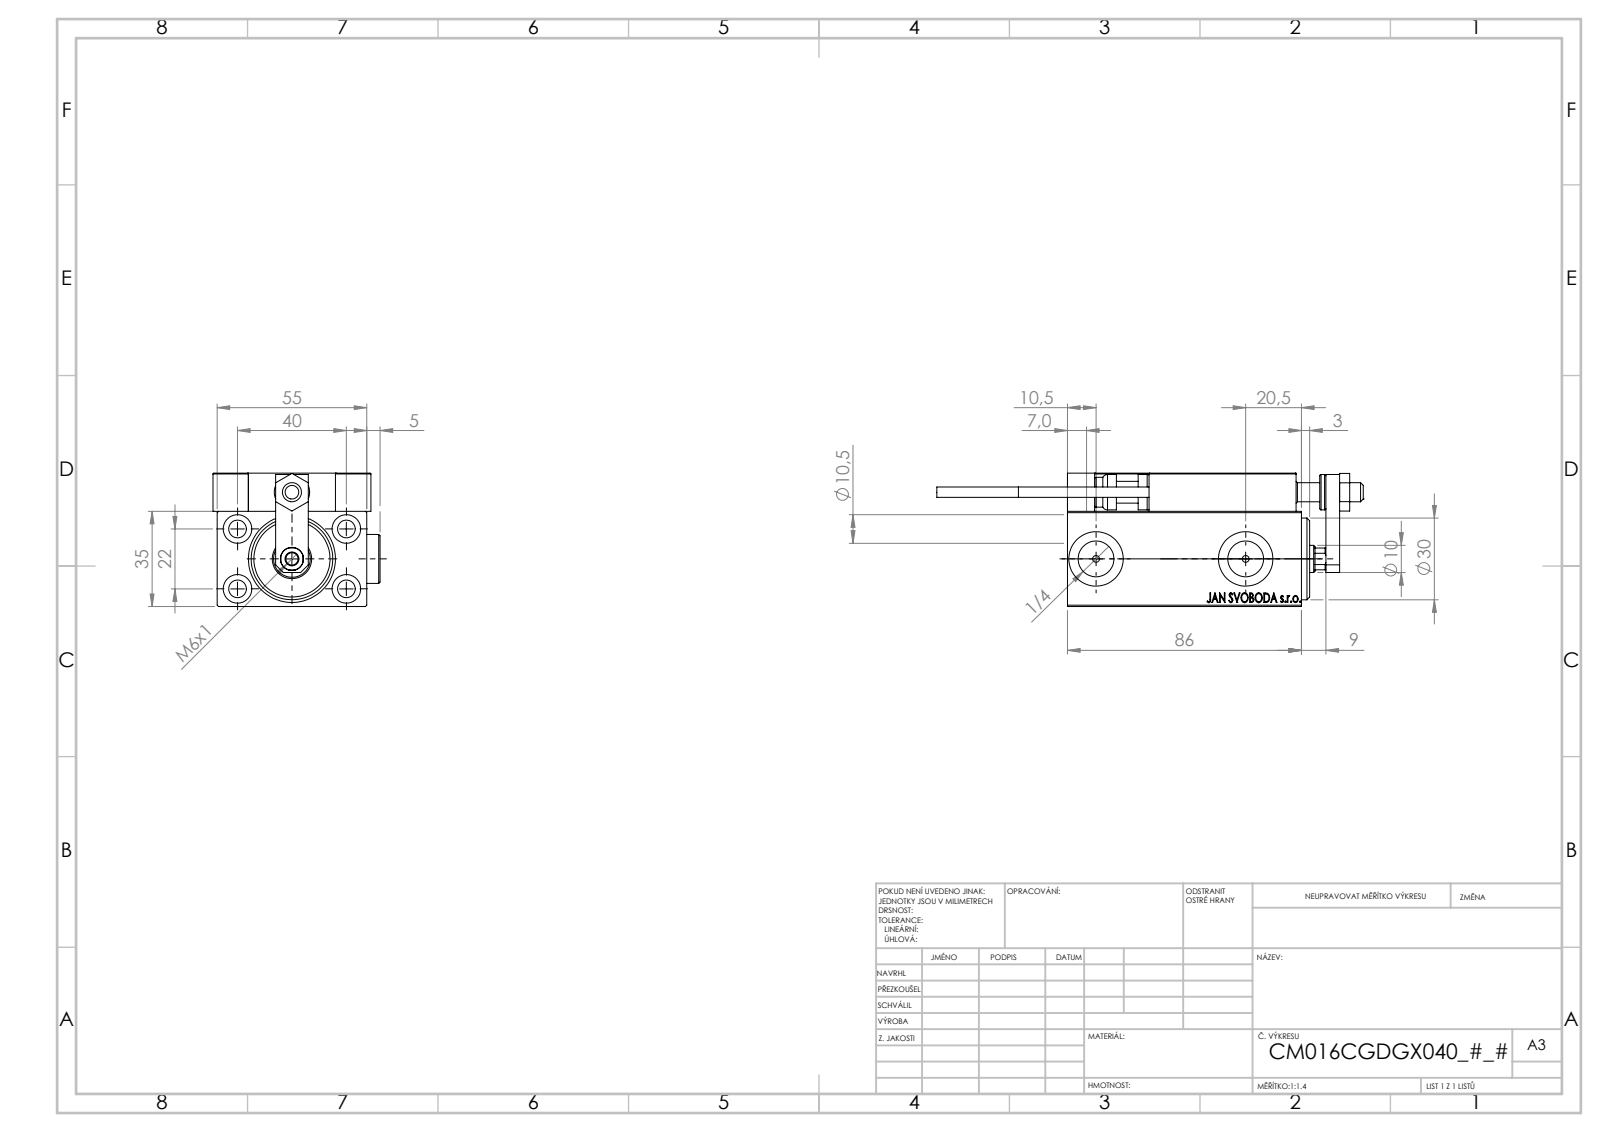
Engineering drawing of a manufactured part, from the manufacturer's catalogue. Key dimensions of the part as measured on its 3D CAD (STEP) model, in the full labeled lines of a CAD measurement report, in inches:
Part name (STEP PRODUCT): NUT_D12; V450CM_C_Body; SWITCH_X_FRONT_BACK; ALLEN BOLT D5 (+7 more)
STEP written by: SolidWorks 2019 (CONFIG_CONTROL_DESIGN)
Units: inches
Bodies: 25 solids, 1339 faces (595 planar, 206 cylindrical, 538 other)
Overall size (bounding box): 6.169 × 2.417 × 1.929
Volume: 11.36 in³ · Surface area: 98.76 in²
Round holes (diameter × count): ⌀0.315 ×5, ⌀0.126 ×4, ⌀0.157 ×4, ⌀0.256 ×4, ⌀0.413 ×4, ⌀0.098 ×2, ⌀0.197 ×2, ⌀0.518 ×2, ⌀0.787 ×2, ⌀0.177 ×1, ⌀0.276 ×1, ⌀0.335 ×1
Round bosses / shafts (diameter × count): ⌀0.709 ×2, ⌀0.197 ×2, ⌀0.15 ×2, ⌀0.512 ×1, ⌀0.433 ×1
Partial cylindrical surfaces — rounded edges, fillets, slot ends (radius × count): R0.012 ×30, R0.118 ×2, R0.177 ×1
Main face-to-face distances: 1.378, 0.197, 0.551, 1.929, 2.165, 0.276, 0.118, 0.394, 0.059, 2.913
Hole centre spacings: 0.899, 0.448, 0.787, 0.866, 0.95, 1.165, 1.169, 1.42
